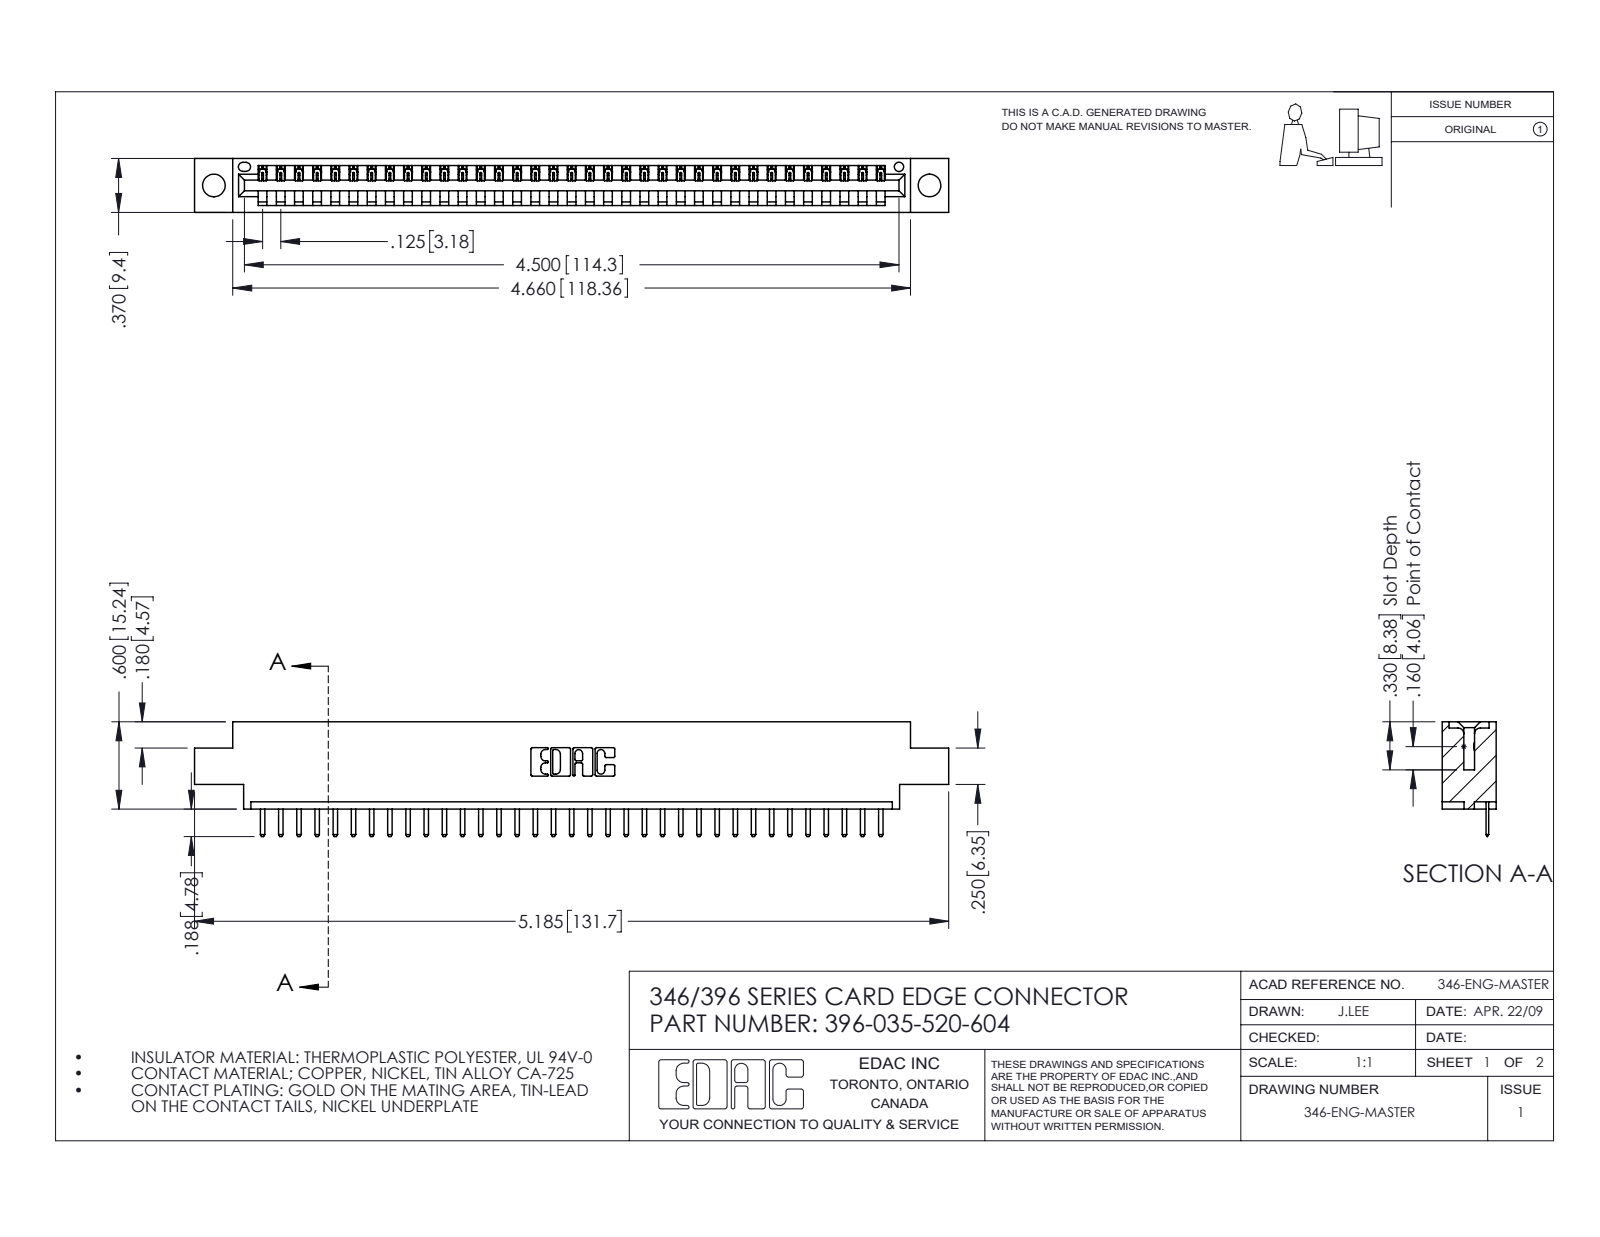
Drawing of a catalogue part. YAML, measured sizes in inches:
part_name: "396-035-520-604; 345-292-001_345-293-120; 346 Part_0.170 Offset - 0.156 Dia-TH"
step_written_by: "SolidWorks 2016 (CONFIG_CONTROL_DESIGN)"
units: inches
bodies: {solids: 36, faces: 2296, planar: 1550, cylindrical: 746, other: 0}
overall_size: [5.185, 0.788, 0.37]
volume: 0.745
surface_area: 22.97
round_holes:
  - {diameter: 0.156, count: 2}
  - {diameter: 0.064, count: 1}
partial_cylinders:
  - {radius: 0.01, count: 72}
  - {radius: 0.006, count: 70}
  - {radius: 0.01, count: 22}
  - {radius: 0.007, count: 6}
  - {radius: 0.031, count: 6}
  - {radius: 0.026, count: 3}
  - {radius: 0.031, count: 2}
  - {radius: 0.04, count: 2}
face_to_face_distances: [0.048, 0.322, 0.37, 0.25, 0.148, 0.222, 0.1, 0.174, 0.072, 0.298]
hole_center_spacings: [0.246, 4.711, 4.92]
